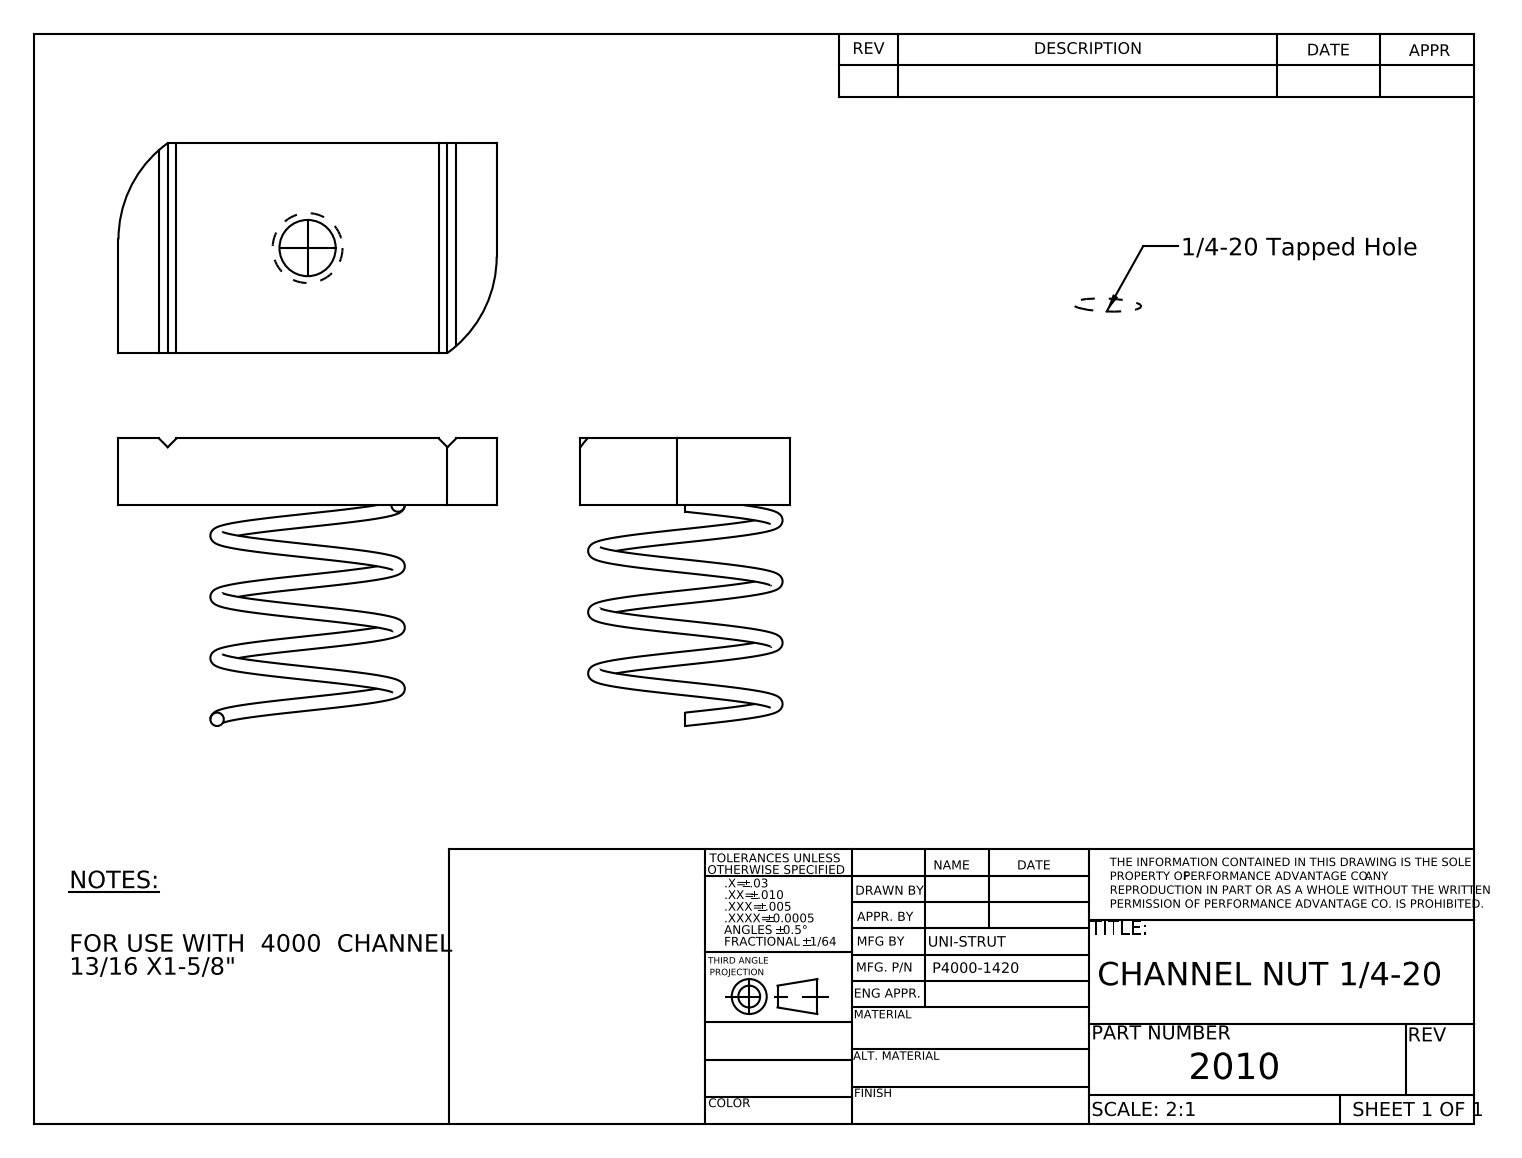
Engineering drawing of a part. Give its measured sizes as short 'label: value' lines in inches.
name: 2010
written by: SolidWorks 2010 (CONFIG_CONTROL_DESIGN)
unit: in
bodies: 1 solid, 20 faces (14 planar, 4 cylindrical, 2 other)
size: 1.352 × 1.028 × 0.75
volume: 0.237 in³; area: 4.08 in²
holes: 1× ⌀0.201
rounds: 2× R0.424
face distances: 0.238, 0.75, 1.352, 0.707, 0.375
